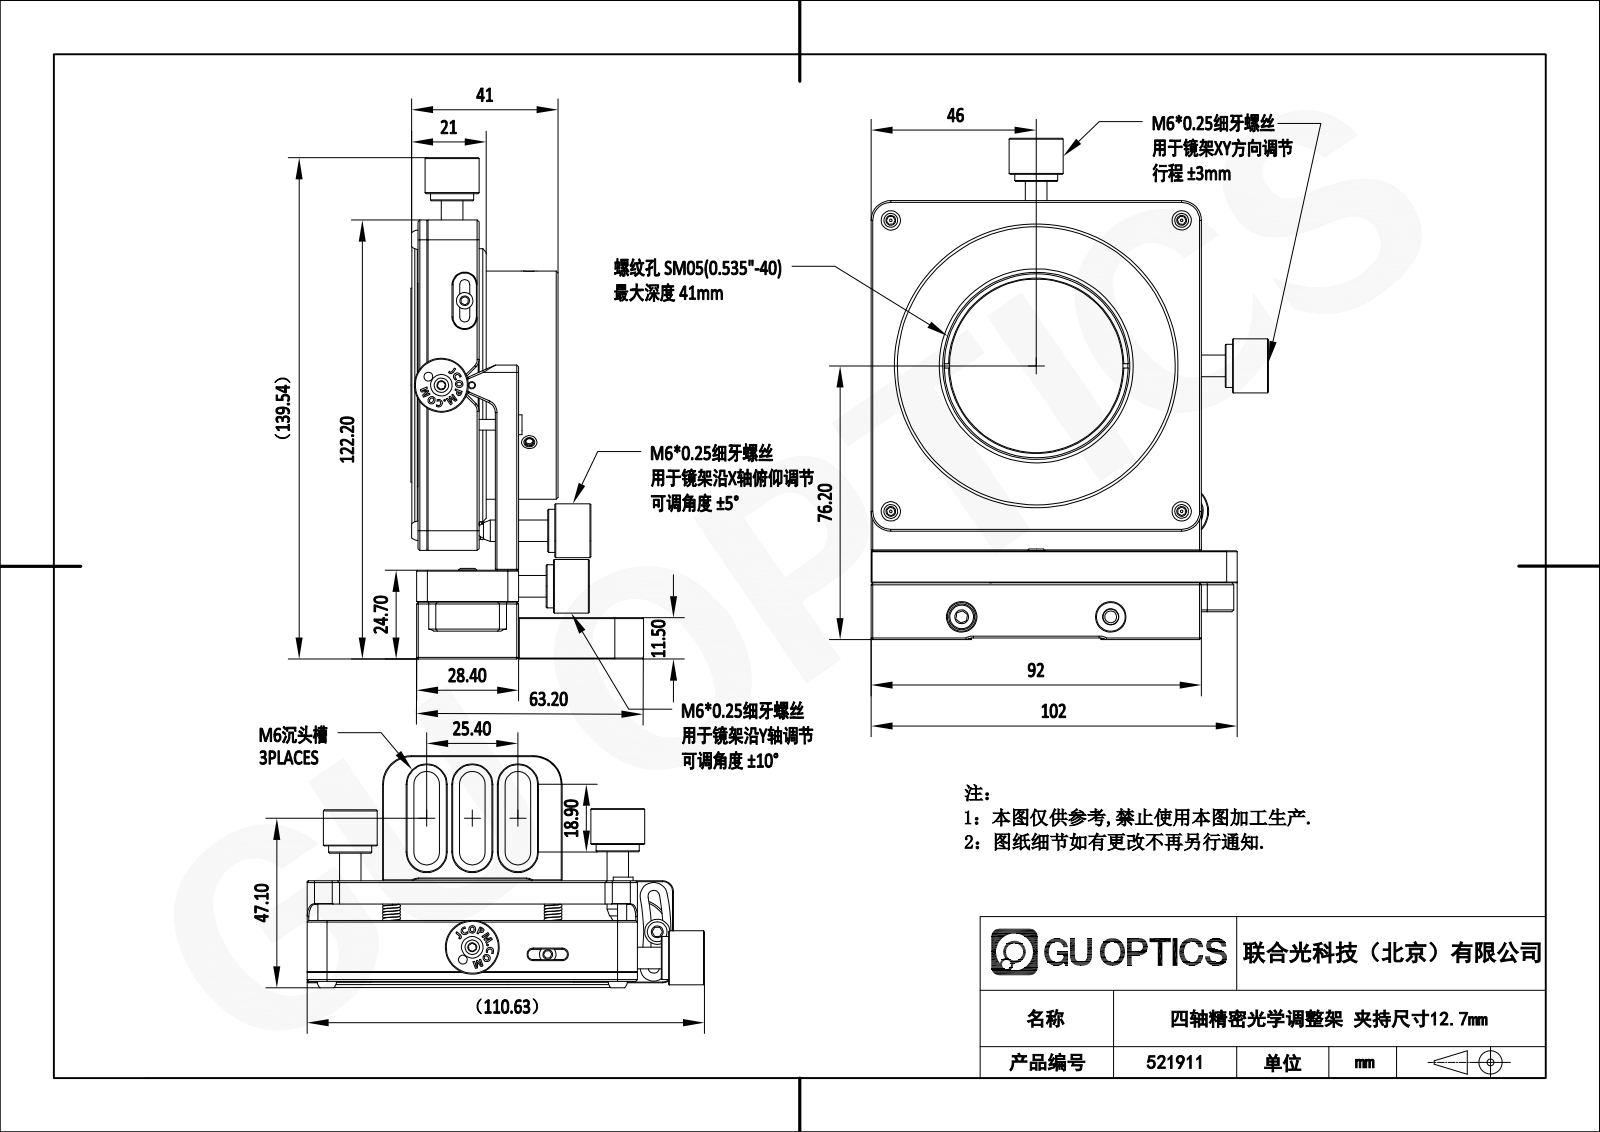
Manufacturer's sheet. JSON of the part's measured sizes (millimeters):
{"part_name": "1.1.10.14_ZJP-Z4SM05", "step_written_by": "SolidWorks 2021 (CONFIG_CONTROL_DESIGN)", "units": "millimeters", "bodies": {"solids": 21, "faces": 1398, "planar": 522, "cylindrical": 364, "other": 512}, "overall_size": [135.34, 103.56, 64.8], "volume_mm3": 258025, "surface_area_mm2": 65732, "round_holes": [[2.5, 10], [1, 8], [3.3, 5], [3.4, 4], [3.5, 4], [3.75, 4], [5.5, 3], [6, 3], [3.2, 2], [4.5, 2], [5, 2], [8, 2]], "round_bosses_or_shafts": [[4, 9], [3, 7], [10, 5], [5, 5], [12, 4], [6.8, 4], [6, 2], [5.5, 2]], "partial_cylinders_radius": [[2, 7], [3, 7], [3.55, 6], [5, 6], [5.45, 6], [2.8, 5], [0.8, 4], [3.25, 4]], "face_to_face_distances": [19, 2, 11, 28, 9, 17, 29.7, 18.7, 92, 21], "hole_center_spacings": [2.6, 81, 5.2, 18, 28, 11.05, 12.5, 13.22]}
